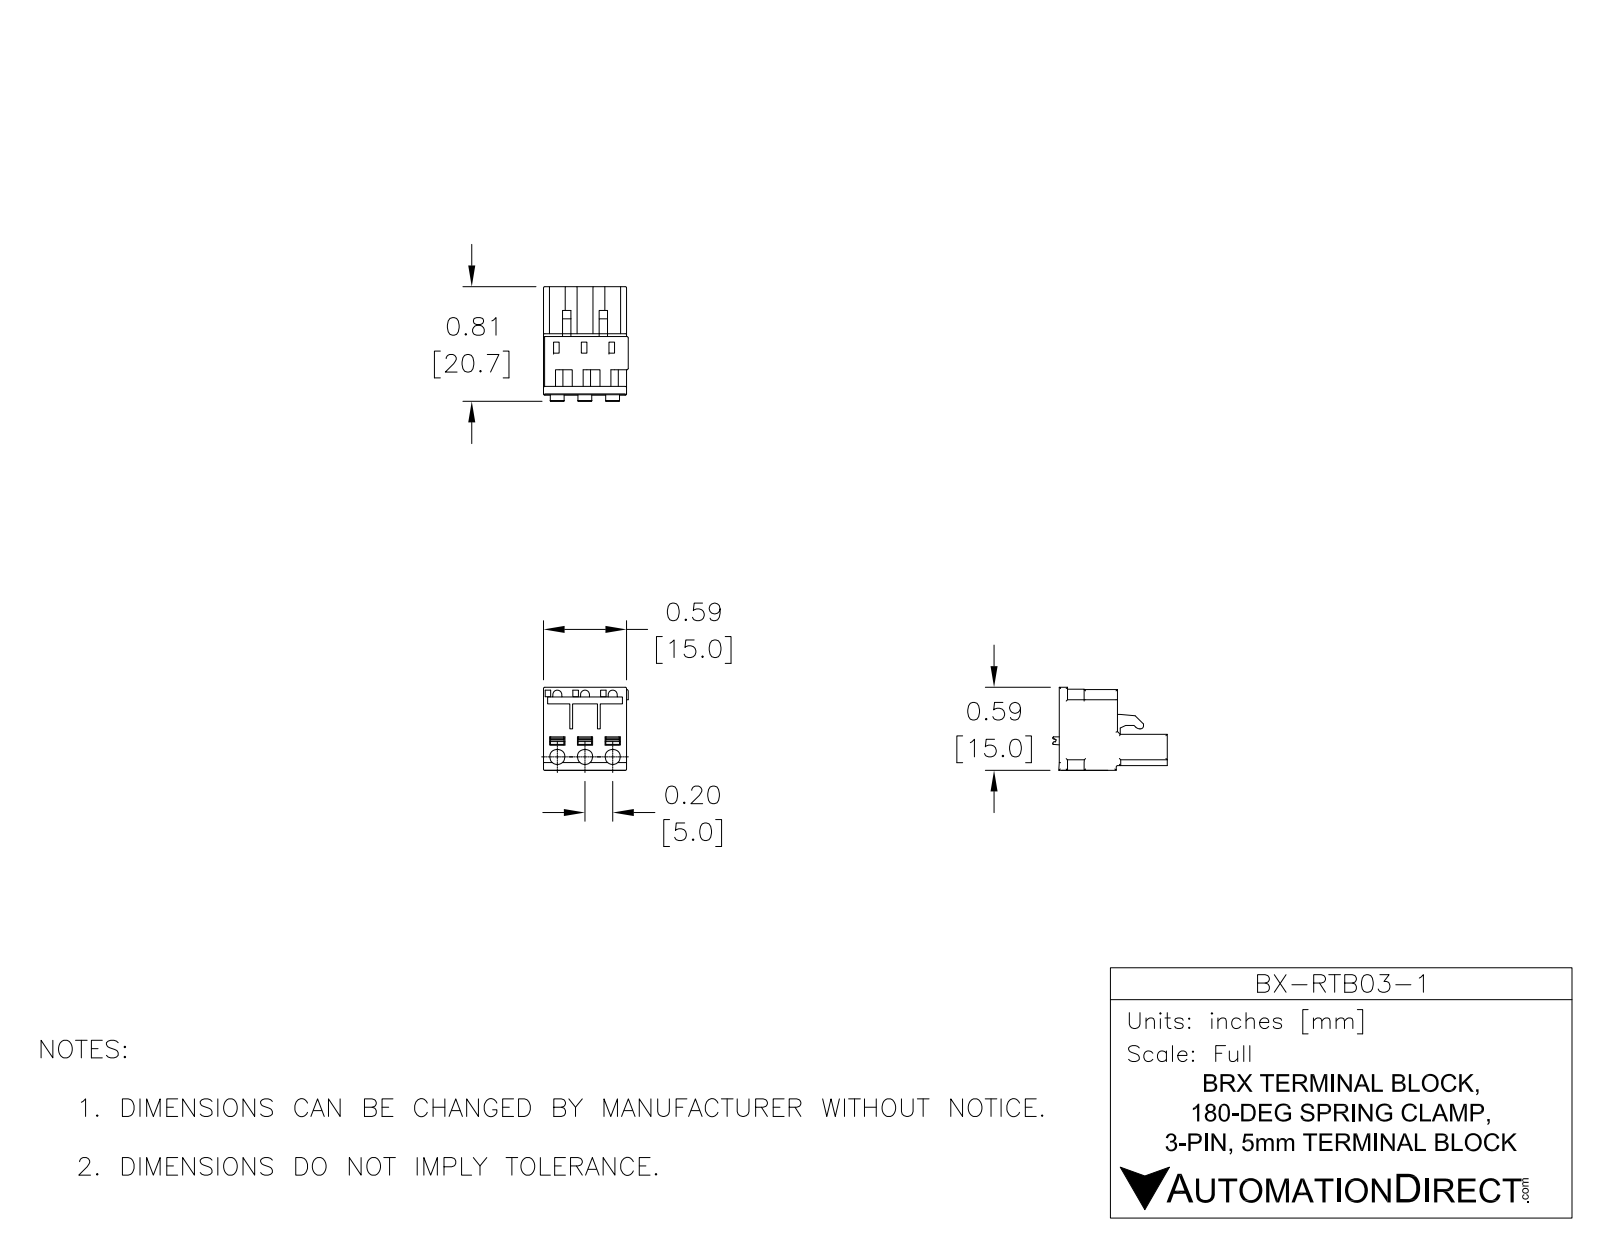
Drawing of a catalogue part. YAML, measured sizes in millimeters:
part_name: "BX-RTB03-1"
step_written_by: "SolidWorks 2016 (AUTOMOTIVE_DESIGN)"
units: millimeters
bodies: {solids: 3, faces: 430, planar: 222, cylindrical: 140, other: 68}
overall_size: [20.7, 15.3, 15]
volume: 2693
surface_area: 2249
round_holes:
  - {diameter: 1.6, count: 3}
  - {diameter: 2.75, count: 3}
  - {diameter: 3.15, count: 3}
partial_cylinders:
  - {radius: 0.25, count: 38}
  - {radius: 0.1, count: 36}
  - {radius: 0.2, count: 4}
  - {radius: 0.8, count: 3}
  - {radius: 1, count: 3}
  - {radius: 2.42, count: 3}
  - {radius: 2.53, count: 3}
  - {radius: 0.27, count: 1}
face_to_face_distances: [15, 14.58, 8.88, 9, 5.7, 10.5, 1.5, 6.5, 5, 8.08]
hole_center_spacings: [5, 5.09, 0.95, 10, 10.05, 0.96]
